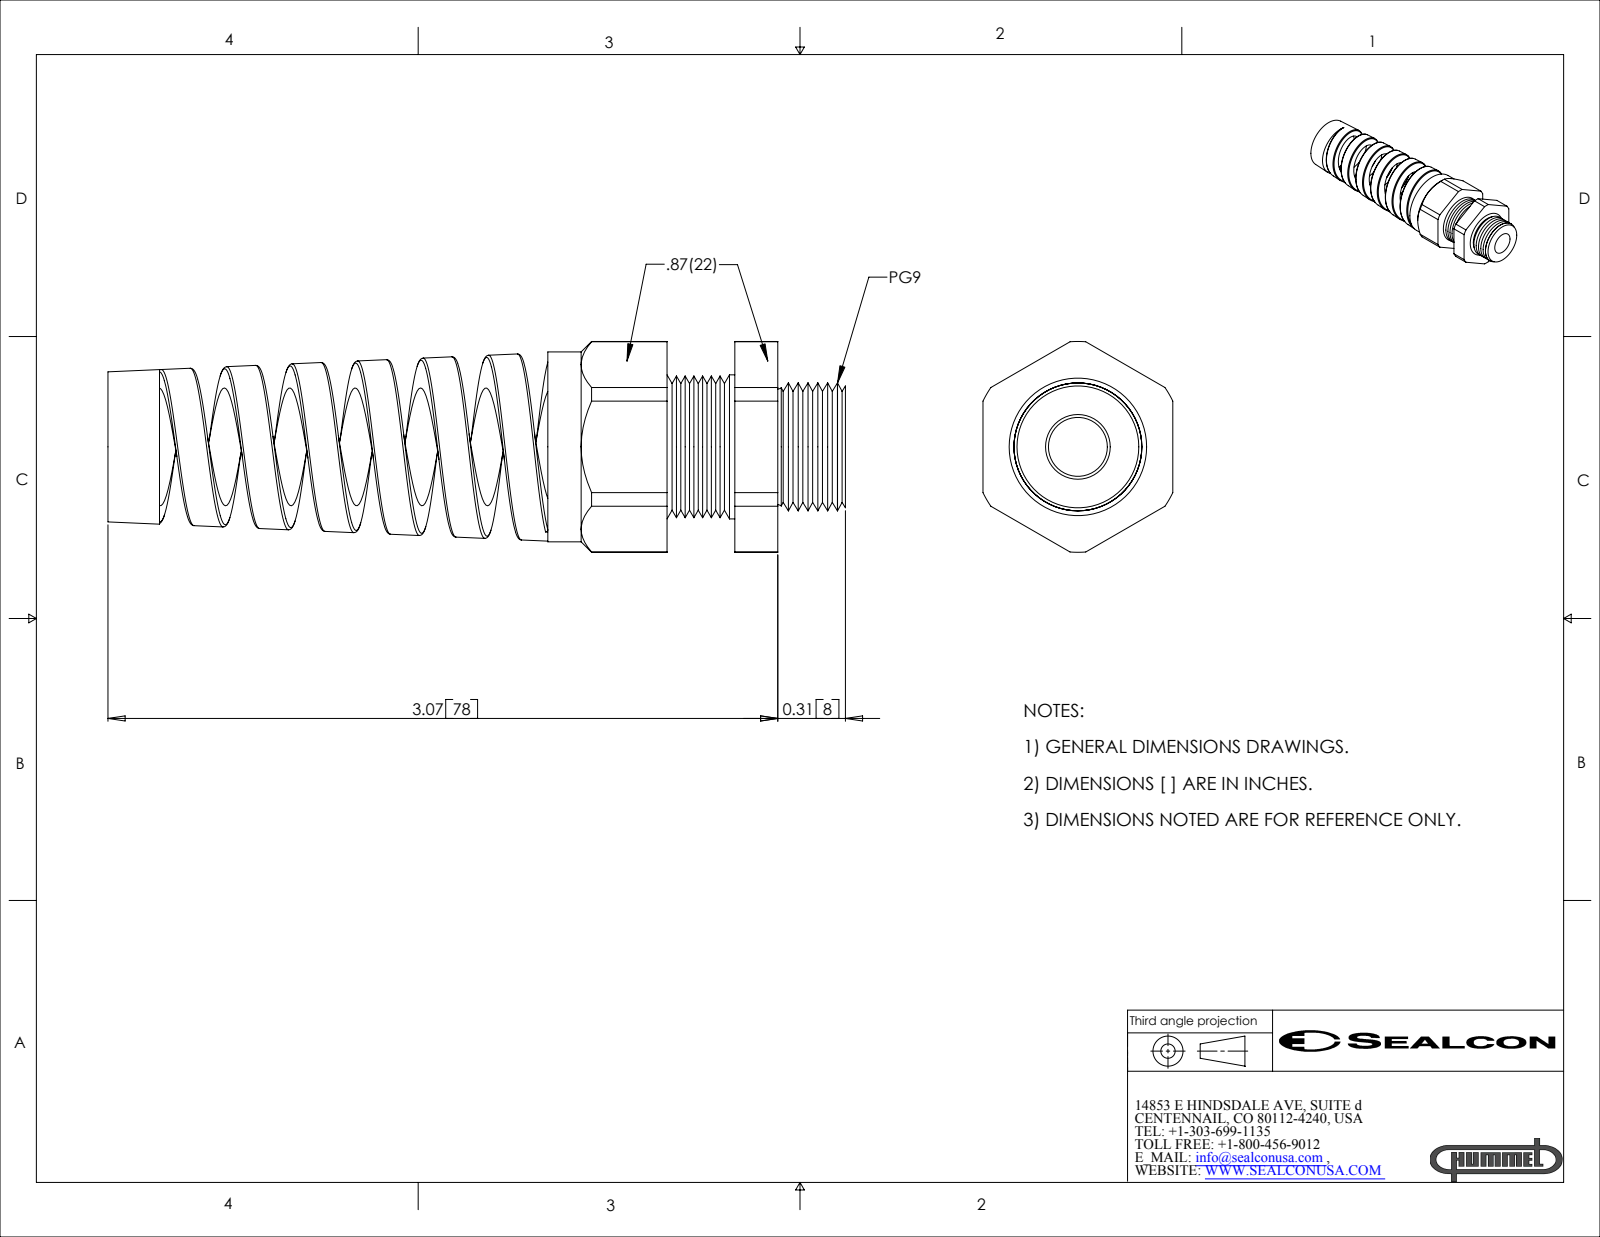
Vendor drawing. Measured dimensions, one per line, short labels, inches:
name: CF09GR-BK
written by: SolidWorks 2007 (CONFIG_CONTROL_DESIGN)
unit: in
bodies: 2 solids, 153 faces (24 planar, 37 cylindrical, 92 other)
size: 3.38 × 0.966 × 0.87
volume: 0.809 in³; area: 17.01 in²
holes: 1× ⌀0.27, 1× ⌀0.54
bosses: 1× ⌀0.87, 1× ⌀0.66
rounds: 1× R0.28, 1× R0.483
face distances: 0.87, 0.508, 0.311, 0.197, 0.818, 0.507, 0.31, 0.546, 0.857, 1.054
